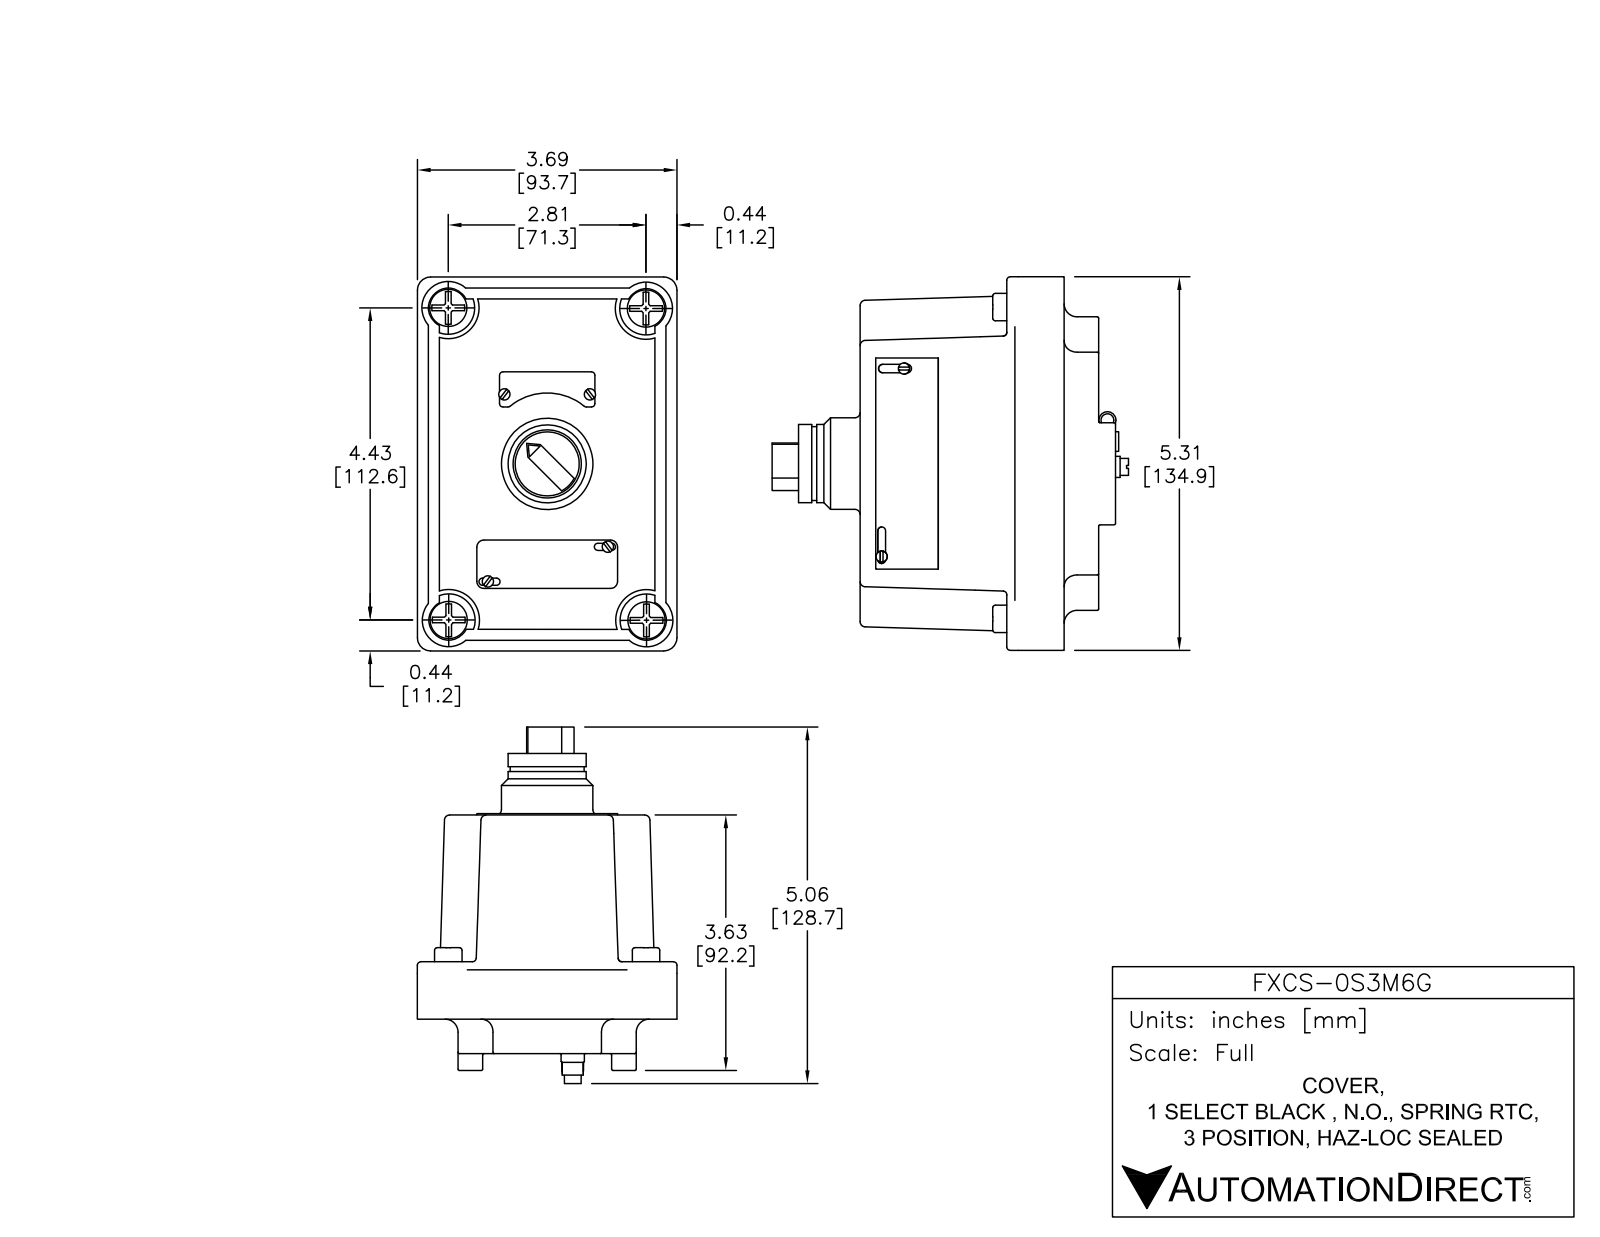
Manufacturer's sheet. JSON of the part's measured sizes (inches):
{"part_name": "FXCS-0S3M6G", "step_written_by": "SolidWorks 2015 (AUTOMOTIVE_DESIGN)", "units": "inches", "bodies": {"solids": 2, "faces": 710, "planar": 308, "cylindrical": 166, "other": 236}, "overall_size": [5.31, 5.066, 3.69], "volume_in3": 48.91, "surface_area_in2": 100.9, "round_holes": [[0.16, 8], [0.198, 1], [0.97, 1]], "round_bosses_or_shafts": [[0.16, 8], [0.39, 4], [1.3, 1], [1.11, 1], [1.05, 1], [0.91, 1], [0.33, 1], [0.3, 1]], "partial_cylinders_radius": [[0.05, 24], [0.02, 22], [0.051, 4], [0.055, 4], [0.06, 4], [0.075, 4], [0.1, 4], [0.185, 4]], "face_to_face_distances": [3.39, 0.49, 2.9, 0.021, 3.69, 0.578, 3.111, 1.19, 0.7, 2.2], "hole_center_spacings": [0.25, 2.197, 0.5, 2.183, 2.239, 0.75, 1.092, 1.115]}
